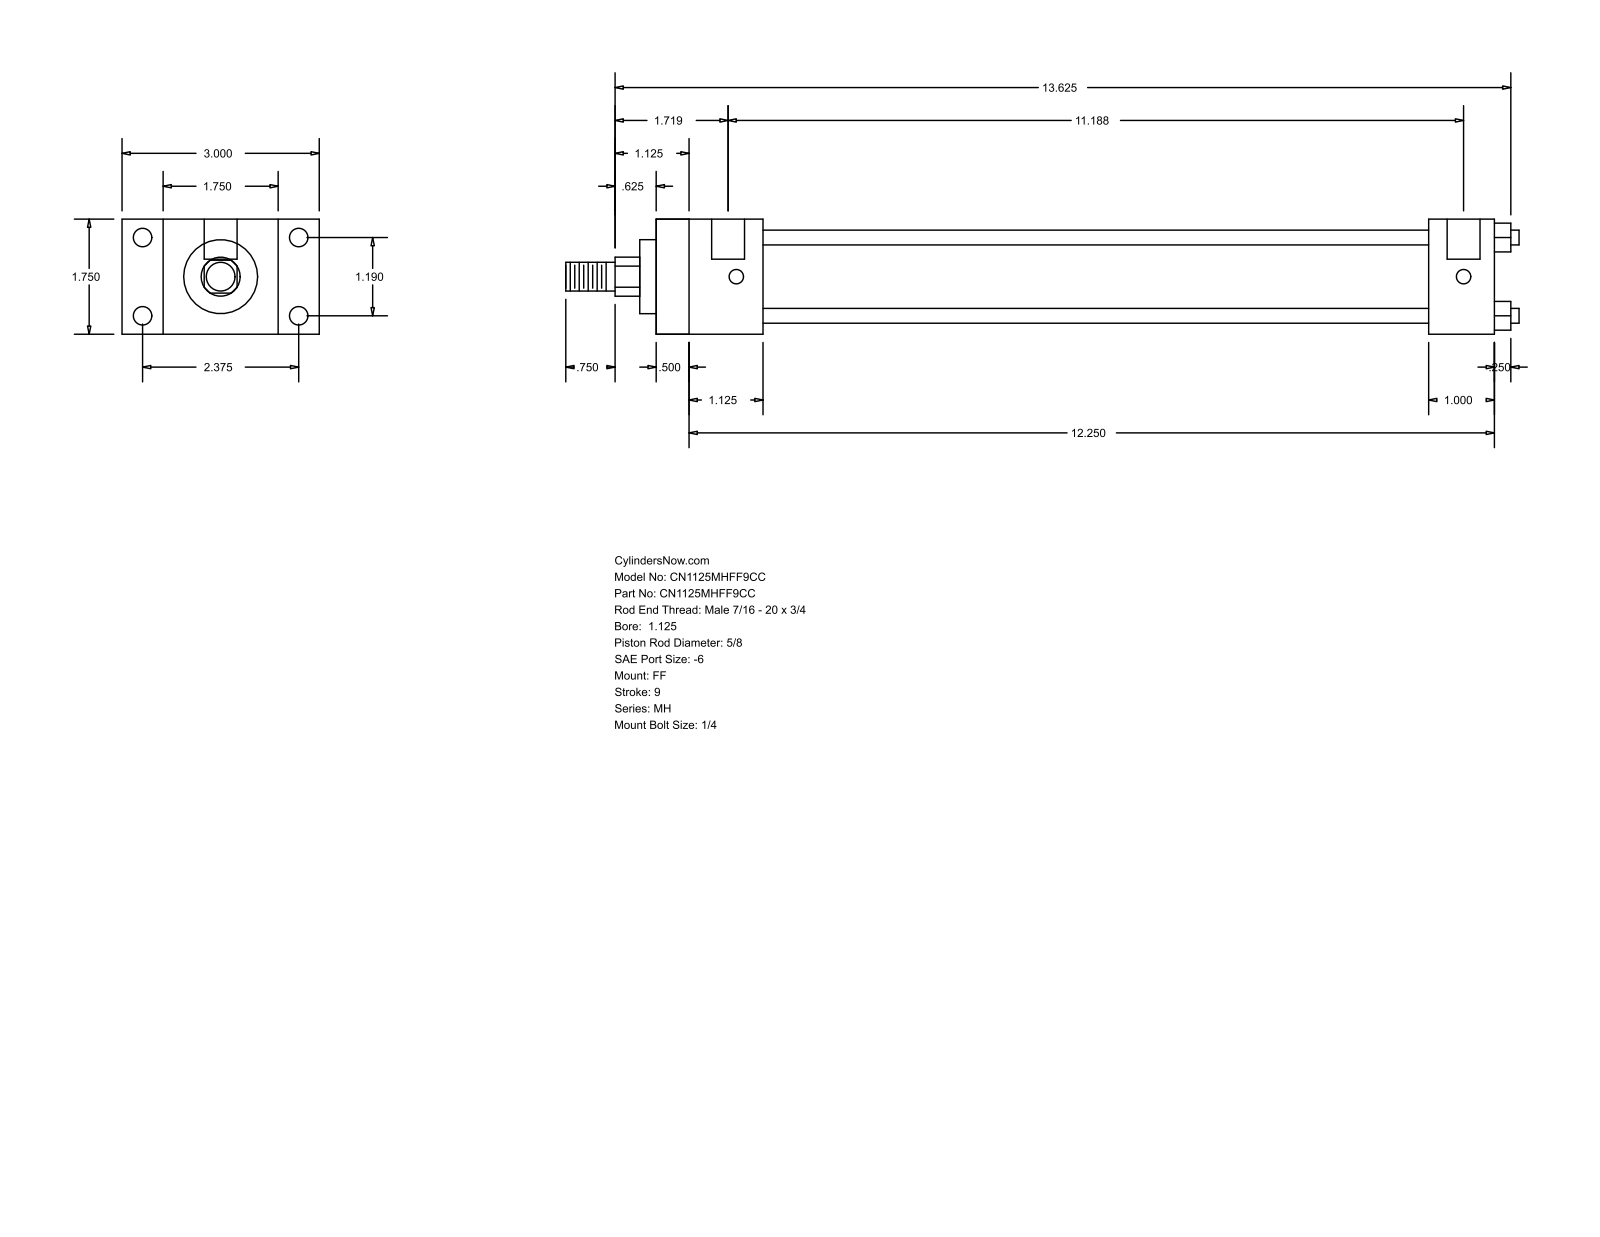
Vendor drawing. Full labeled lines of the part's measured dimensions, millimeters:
Part name (STEP PRODUCT): MH_FF__0112_0.625
STEP written by: GSSL Pune (CONFIG_CONTROL_DESIGN)
Units: millimetres
Bodies: 0 solids, 92 faces (64 planar, 28 cylindrical, 0 other)
Overall size (bounding box): 368.3 × 76.2 × 44.45
Round holes (diameter × count): ⌀5.56 ×4, ⌀7.14 ×4, ⌀12.7 ×2
Round bosses / shafts (diameter × count): ⌀5.71 ×4, ⌀34.92 ×1, ⌀28.57 ×1, ⌀15.88 ×1, ⌀11.11 ×1
Partial cylindrical surfaces — rounded edges, fillets, slot ends (radius × count): R7.54 ×1
Main face-to-face distances: 44.46, 323.85, 12.69, 311.16, 15.87, 28.58, 60.33, 41.27, 298.44, 285.75
Hole centre spacings: 30.22, 60.32, 67.47, 280.99, 3.17, 284.16
